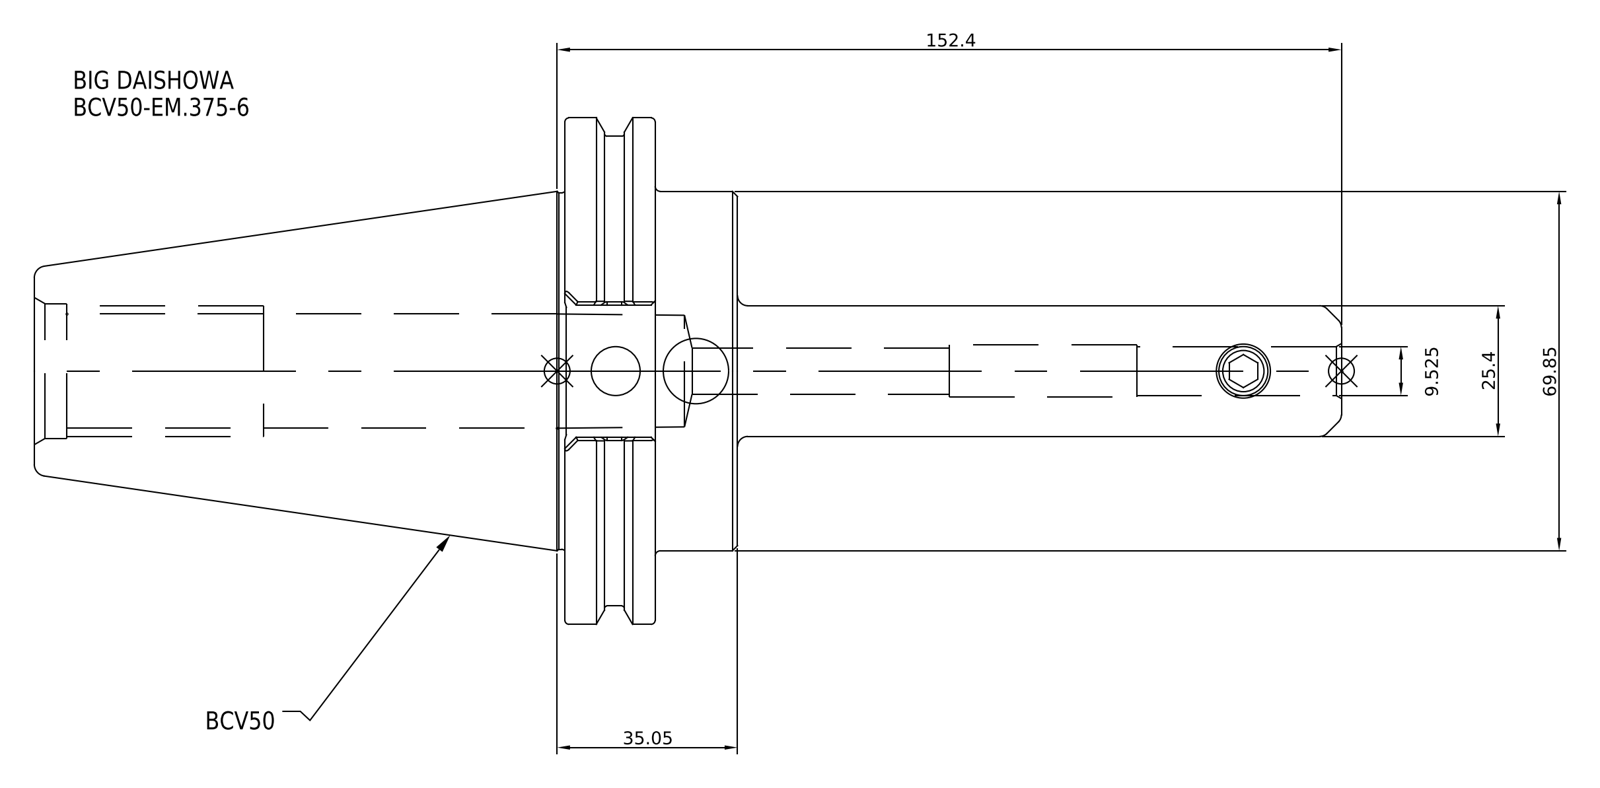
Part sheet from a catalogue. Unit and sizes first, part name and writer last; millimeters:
Units: millimetres
Overall size (bounding box): 254 × 98.43 × 98.43
Round holes (diameter × count): ⌀9.53 ×1
Round bosses / shafts (diameter × count): ⌀98.43 ×1, ⌀91.29 ×1, ⌀69.85 ×1, ⌀25.4 ×1
Main face-to-face distances: 17.55, 16, 33.55, 136.65, 120.65, 103.1, 25.85, 9.85, 7.7, 110.8
Volume: 493 344 mm³ · Surface area: 53 688 mm²
Bodies: 1 solid, 30 faces (8 planar, 14 cylindrical, 8 other)
Part name (STEP PRODUCT): BCV50-EM_375-6
STEP written by: SolidWorks 2021 (CONFIG_CONTROL_DESIGN)
